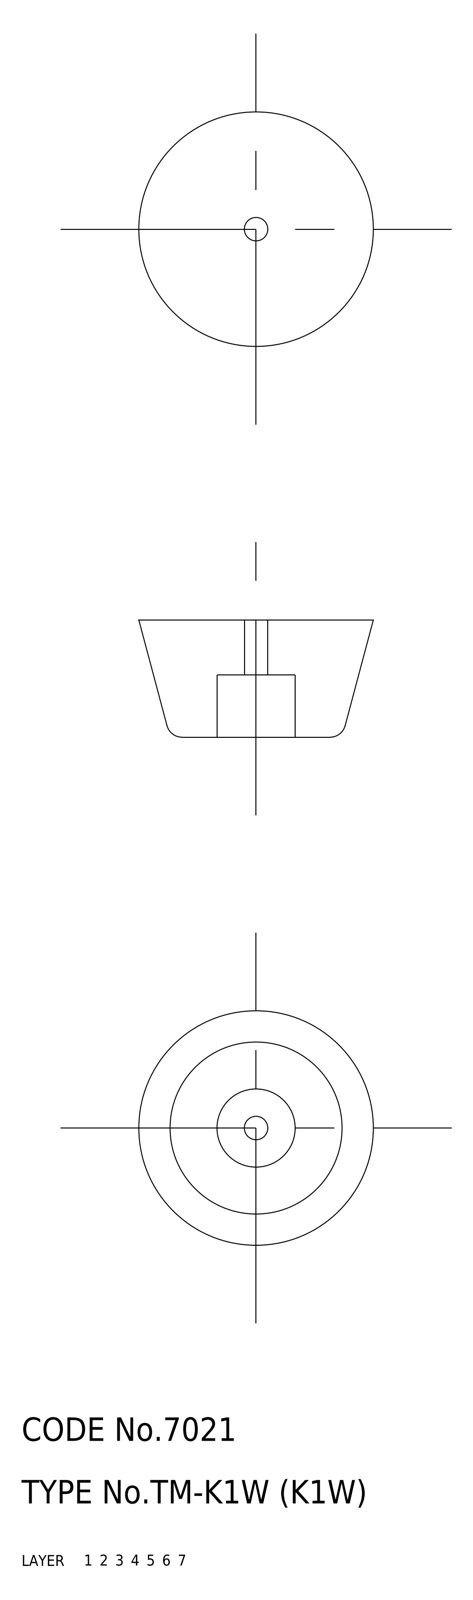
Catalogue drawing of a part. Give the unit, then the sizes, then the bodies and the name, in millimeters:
Units: millimetres
Overall size (bounding box): 30 × 30 × 15
Volume: 7 335 mm³ · Surface area: 2 964 mm²
Bodies: 2 solids, 23 faces (0 planar, 0 cylindrical, 23 other)
Part name (STEP PRODUCT): washer; rubber foot; K1W_6231_36
STEP written by: CADfix (AUTOMOTIVE_DESIGN)
